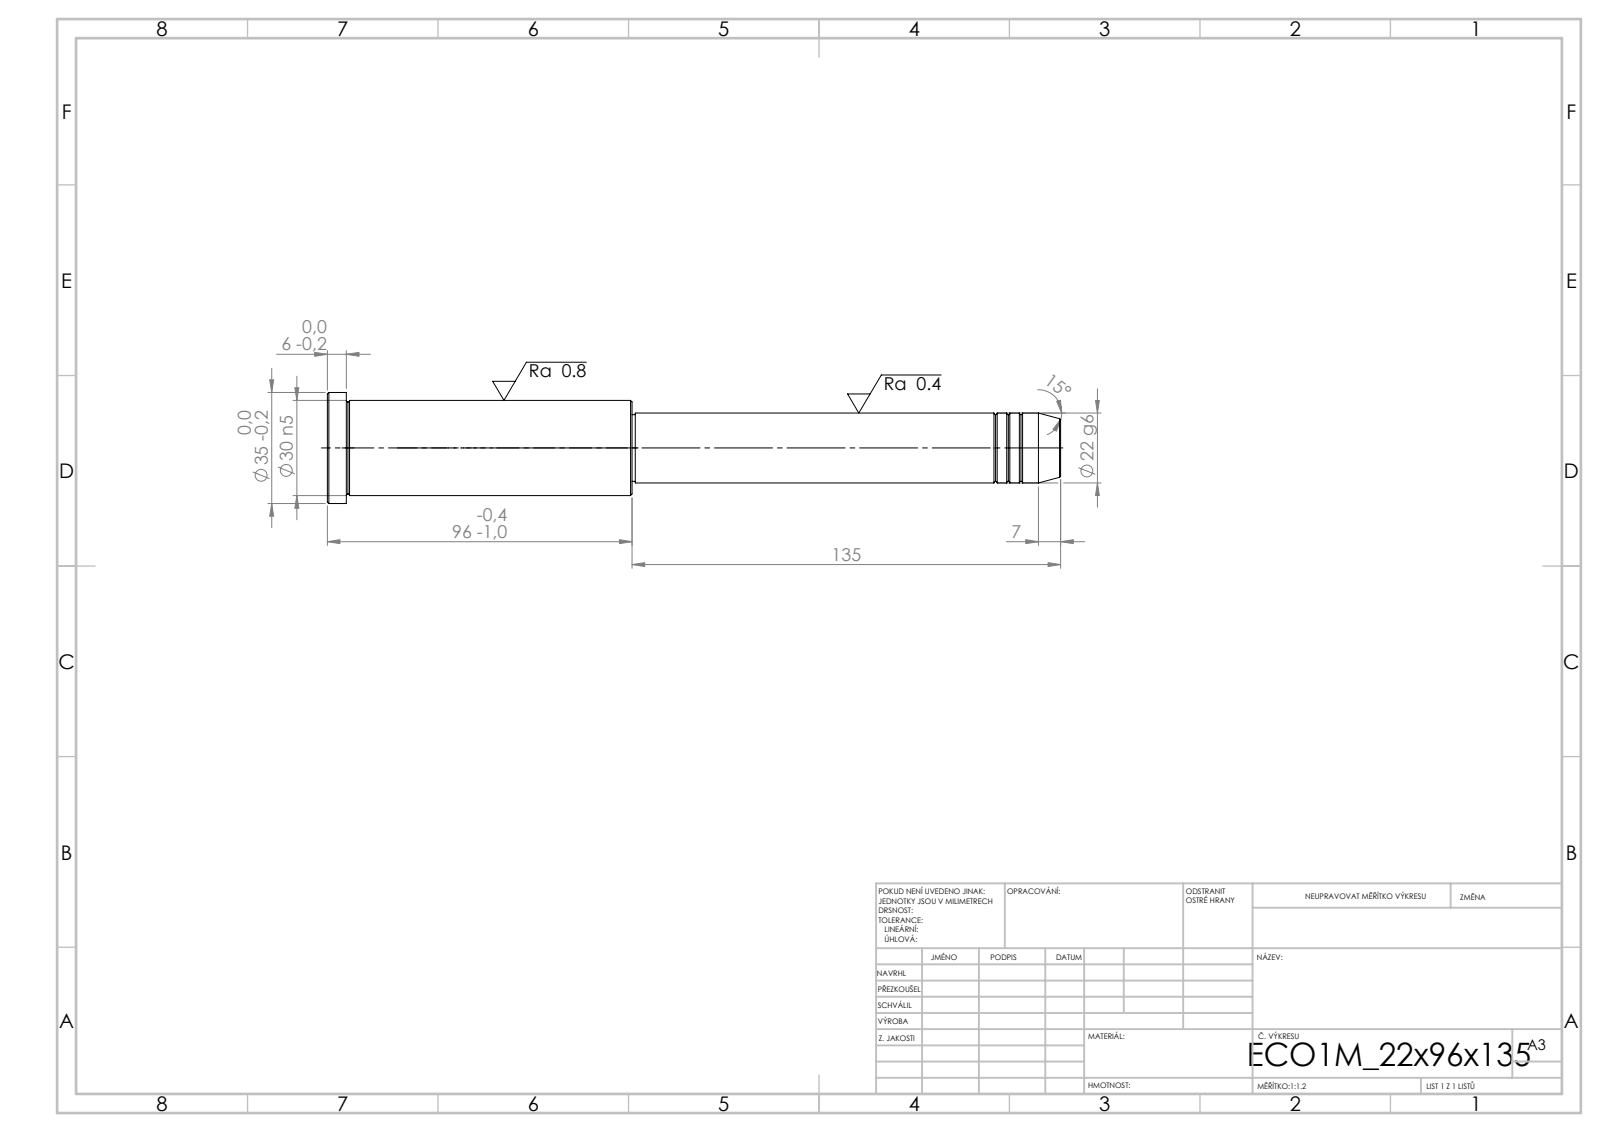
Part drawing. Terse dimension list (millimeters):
written by: SolidWorks 2019 (CONFIG_CONTROL_DESIGN)
unit: mm
bodies: 1 solid, 43 faces (5 planar, 14 cylindrical, 24 other)
size: 231 × 35 × 35
volume: 120 103 mm³; area: 20 410 mm²
bosses: 1× ⌀35, 1× ⌀30, 1× ⌀22, 1× ⌀21
face distances: 96, 90, 6, 135, 225, 231, 134, 1, 91, 97
